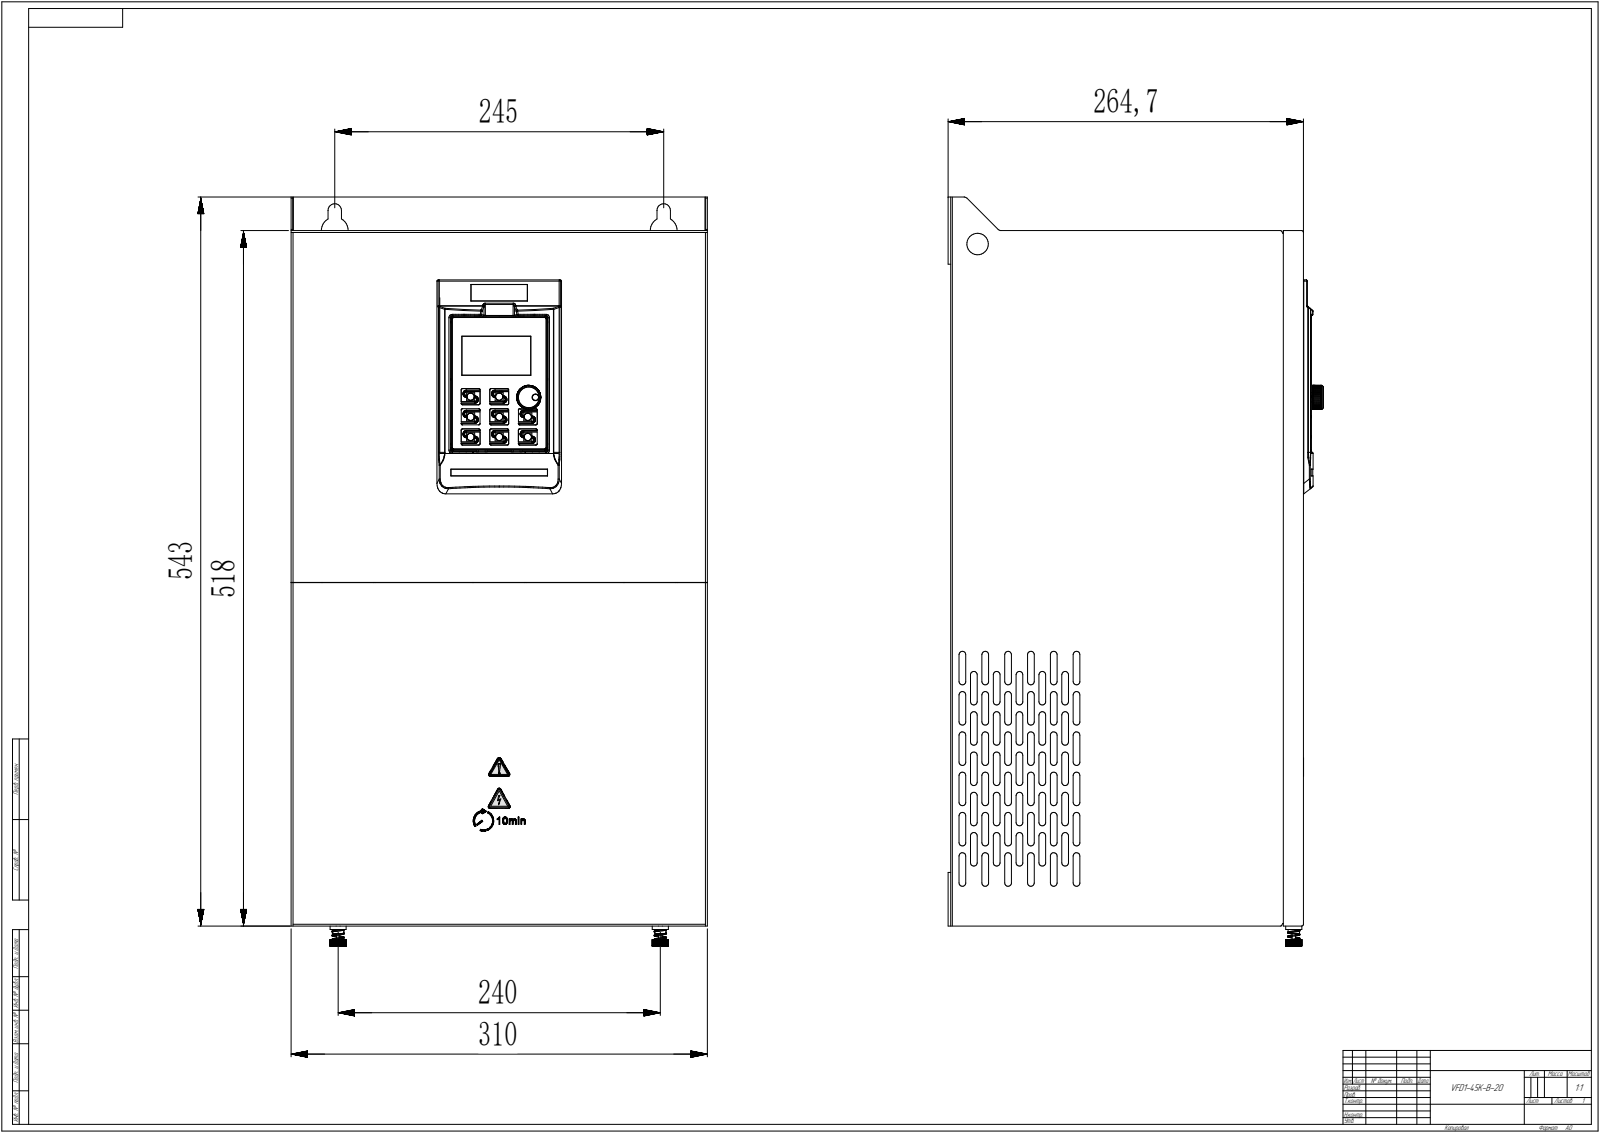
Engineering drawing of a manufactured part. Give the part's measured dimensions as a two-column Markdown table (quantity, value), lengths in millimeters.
| quantity | value |
| --- | --- |
| part name | VM1000B-122-201_333; S-M4-ZC_543; VM1000B-122-201_ASM_333_ASM; VM1000B-122-202_329 (+8 more) |
| STEP written by | CREO PARAMETRIC BY PTC INC, 2020074 (CONFIG_CONTROL_DESIGN) |
| units | millimeters |
| bodies | 185 solids, 16945 faces (12556 planar, 3102 cylindrical, 1287 other) |
| overall size | 558 × 310 × 279.6 |
| volume | 2 163 000 mm³ |
| surface area | 2 592 000 mm² |
| round holes (diameter × count) | 4 × 95, 5.4 × 38, 5.2 × 30, 5 × 24, 6 × 16, 4.5 × 15, 7 × 15, 5.5 × 12, 11 × 11, 6.1 × 9, 10 × 9, 4.1 × 8 |
| round bosses / shafts (diameter × count) | 8 × 46, 5.38 × 46, 2 × 22, 1.2 × 19, 0.5 × 14, 12 × 11, 5.95 × 11, 4.8 × 11 |
| partial cylindrical surfaces (radius × count) | 2.5 × 380, 2 × 159, 0.5 × 141, 1 × 118, 0.34 × 35, 1.7 × 35, 1.3 × 28, 5 × 27 |
| main face-to-face distances | 1.2, 261.5, 308.8, 102.5, 159, 260.3, 307.6, 262.7, 47.3, 160.7 |
| hole center spacings | 82.5, 30.32, 116.67, 130, 153.97, 172.78, 264, 23.6 |
